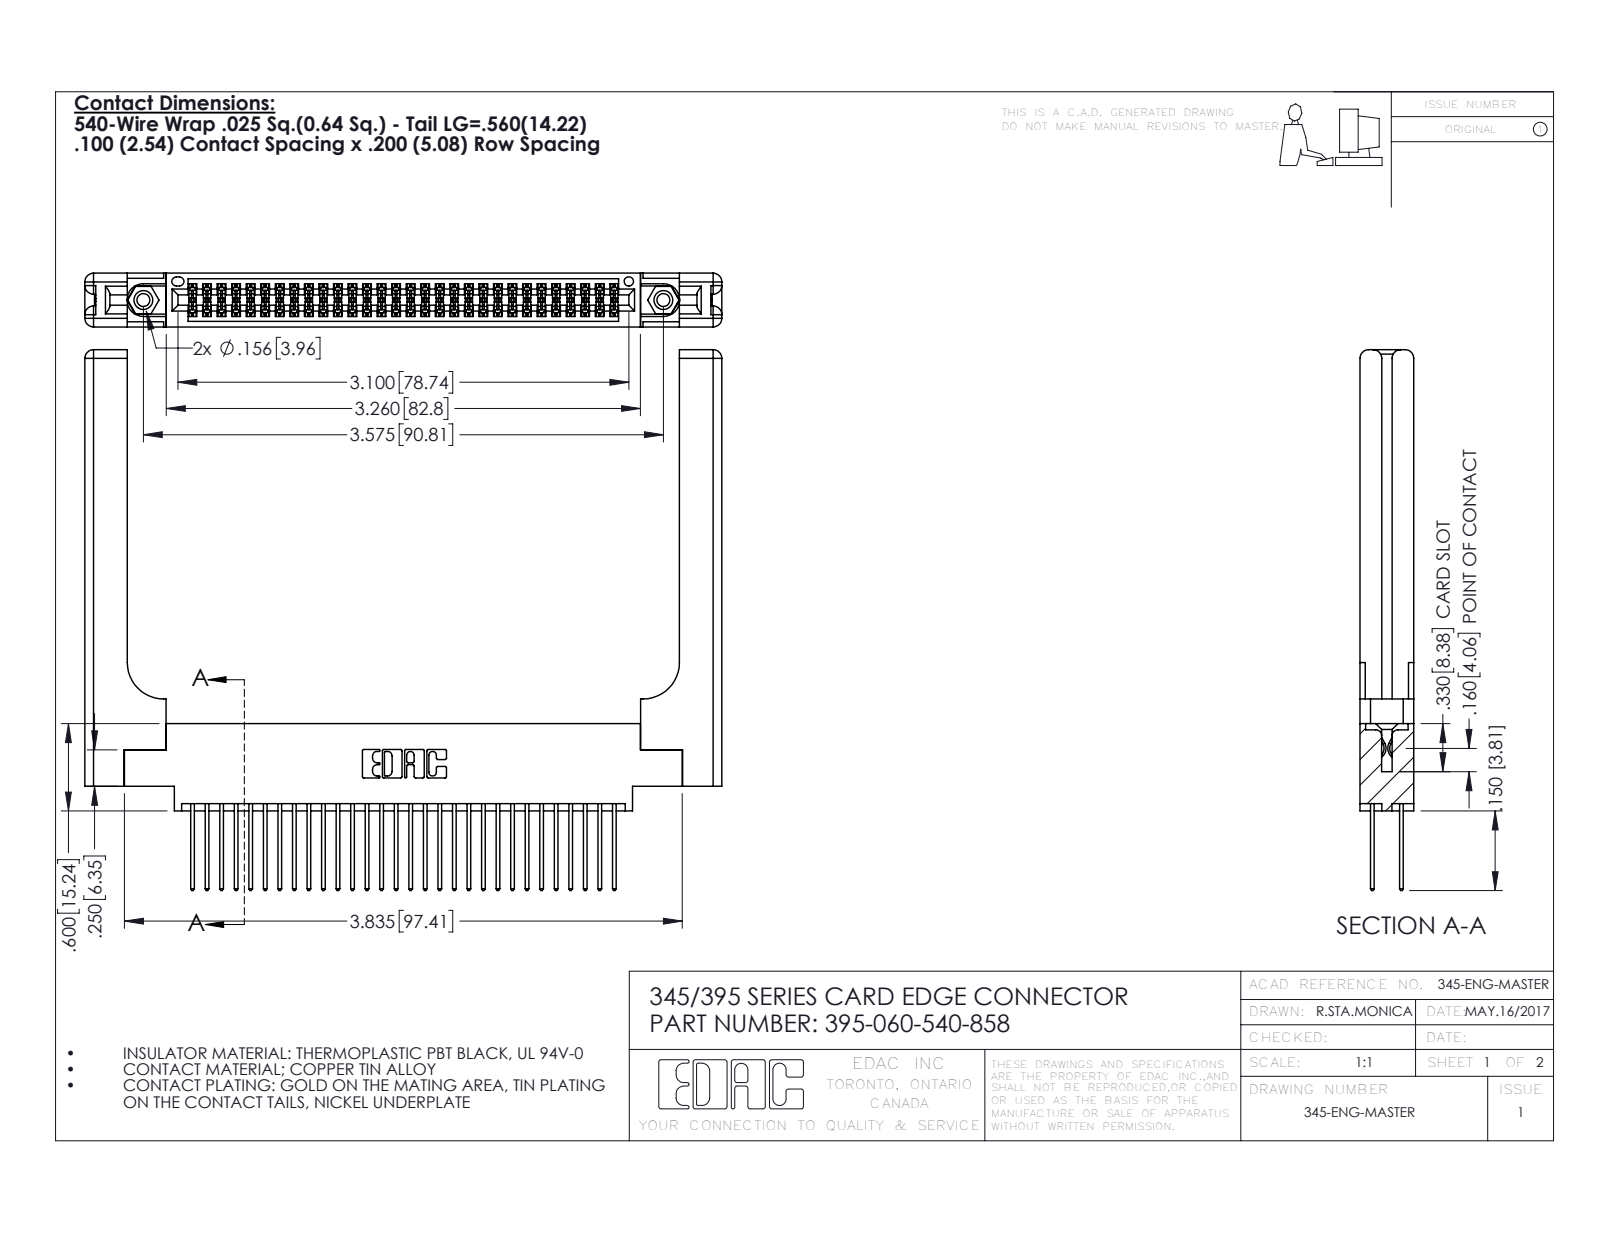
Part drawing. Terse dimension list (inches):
name: 345-220-058_345-220-058; 345-250-001_345-250-001-102; 345 Part_0.170 Offset - 0.156 Dia-TH; 345-292-001_345-293-140 (+1 more)
written by: SolidWorks 2016 (CONFIG_CONTROL_DESIGN)
unit: in
bodies: 65 solids, 3386 faces (2212 planar, 1114 cylindrical, 60 other)
size: 4.379 × 3.717 × 0.37
volume: 1.177 in³; area: 34.1 in²
holes: 2× ⌀0.089, 2× ⌀0.125, 2× ⌀0.156, 1× ⌀0.064
bosses: 2× ⌀0.155
rounds: 90× R0.006, 60× R0.01, 22× R0.01, 16× R0.06, 6× R0.007, 6× R0.031, 3× R0.026, 2× R0.014
face distances: 0.072, 0.37, 0.298, 0.098, 0.272, 0.025, 0.2, 0.225, 0.148, 0.15
hole spacings: 0.27, 3.34, 3.575
